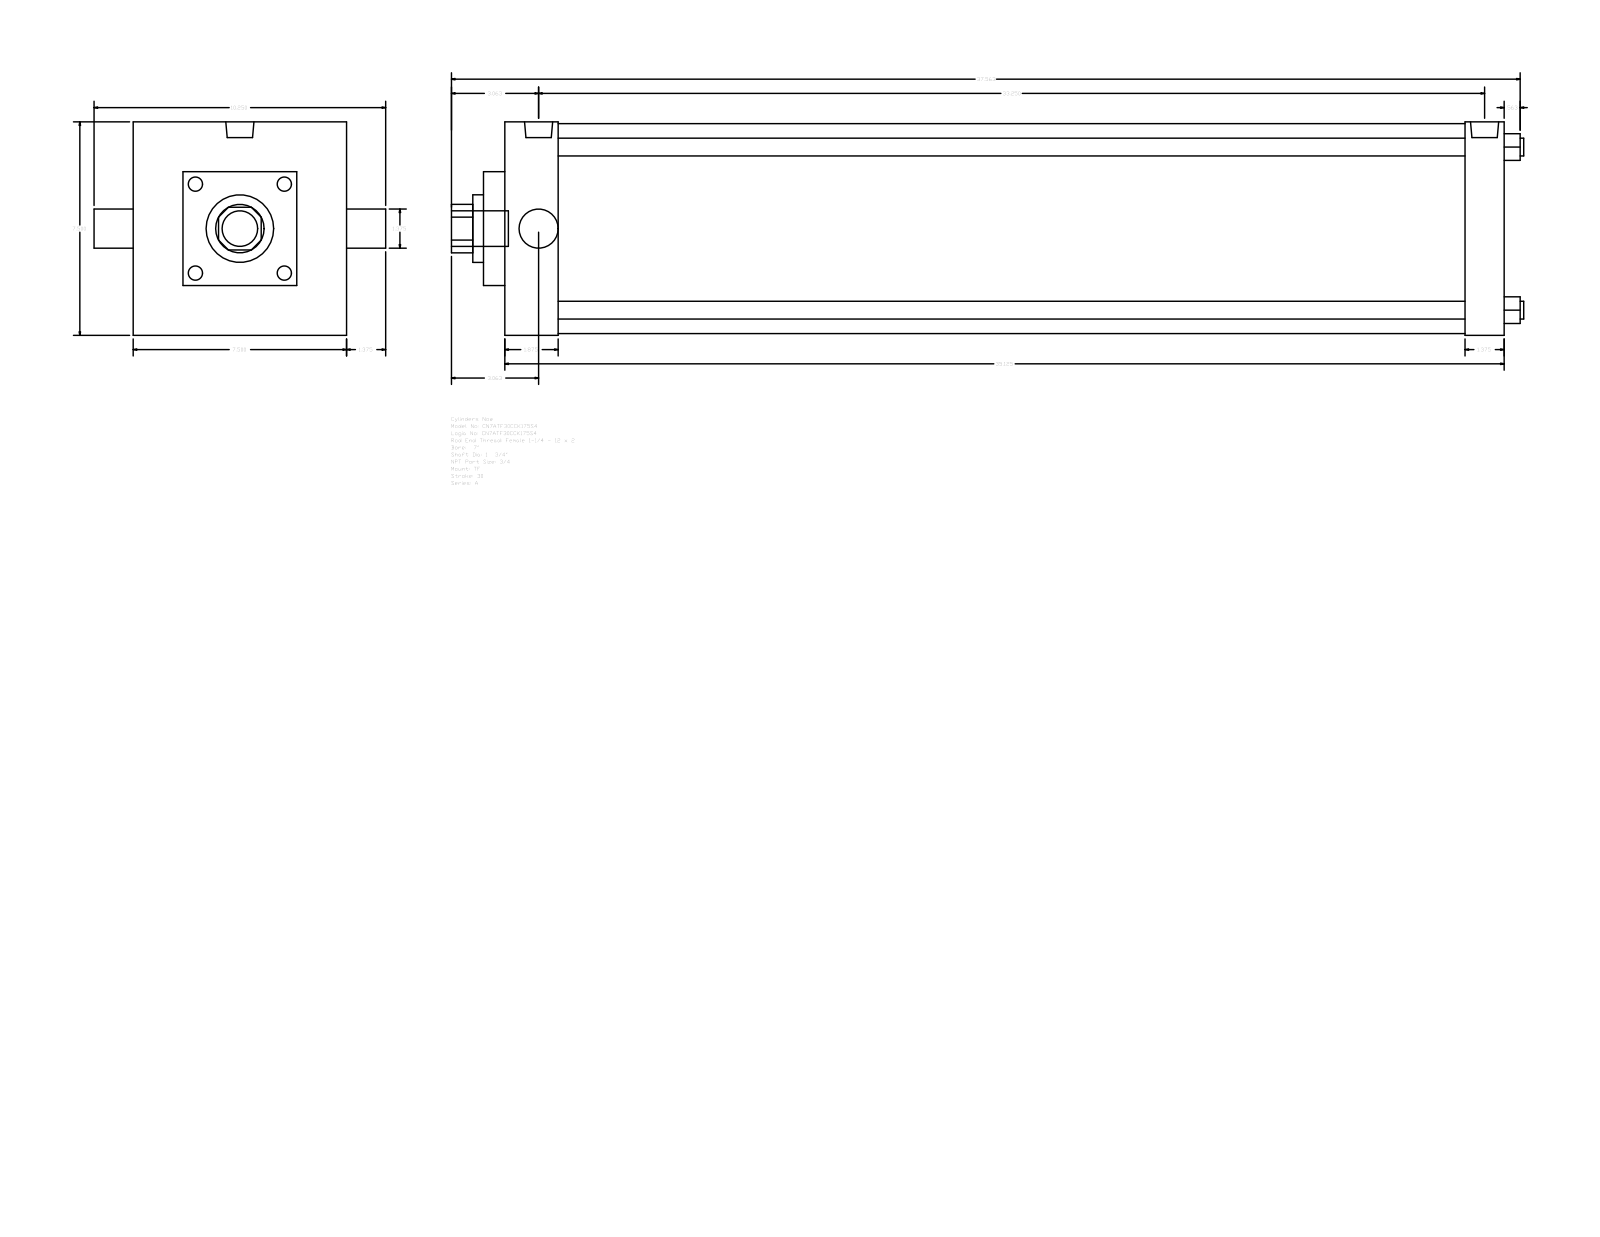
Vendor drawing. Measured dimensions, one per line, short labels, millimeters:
name: A_TF__0700_1.75
written by: GSSL Pune (CONFIG_CONTROL_DESIGN)
unit: mm
bodies: 0 solids, 89 faces (65 planar, 24 cylindrical, 0 other)
size: 957.26 × 260.35 × 190.5
holes: 4× ⌀15.88, 1× ⌀34.92, 1× ⌀44.45, 1× ⌀60.33, 1× ⌀187.32
bosses: 3× ⌀15.08, 2× ⌀25.12, 1× ⌀31.75
rounds: 1× R21.63
face distances: 190.5, 892.18, 44.45, 34.92, 19.05, 47.63, 844.55, 857.26, 809.63, 146.05
hole spacings: 102.91, 145.54, 205.82
